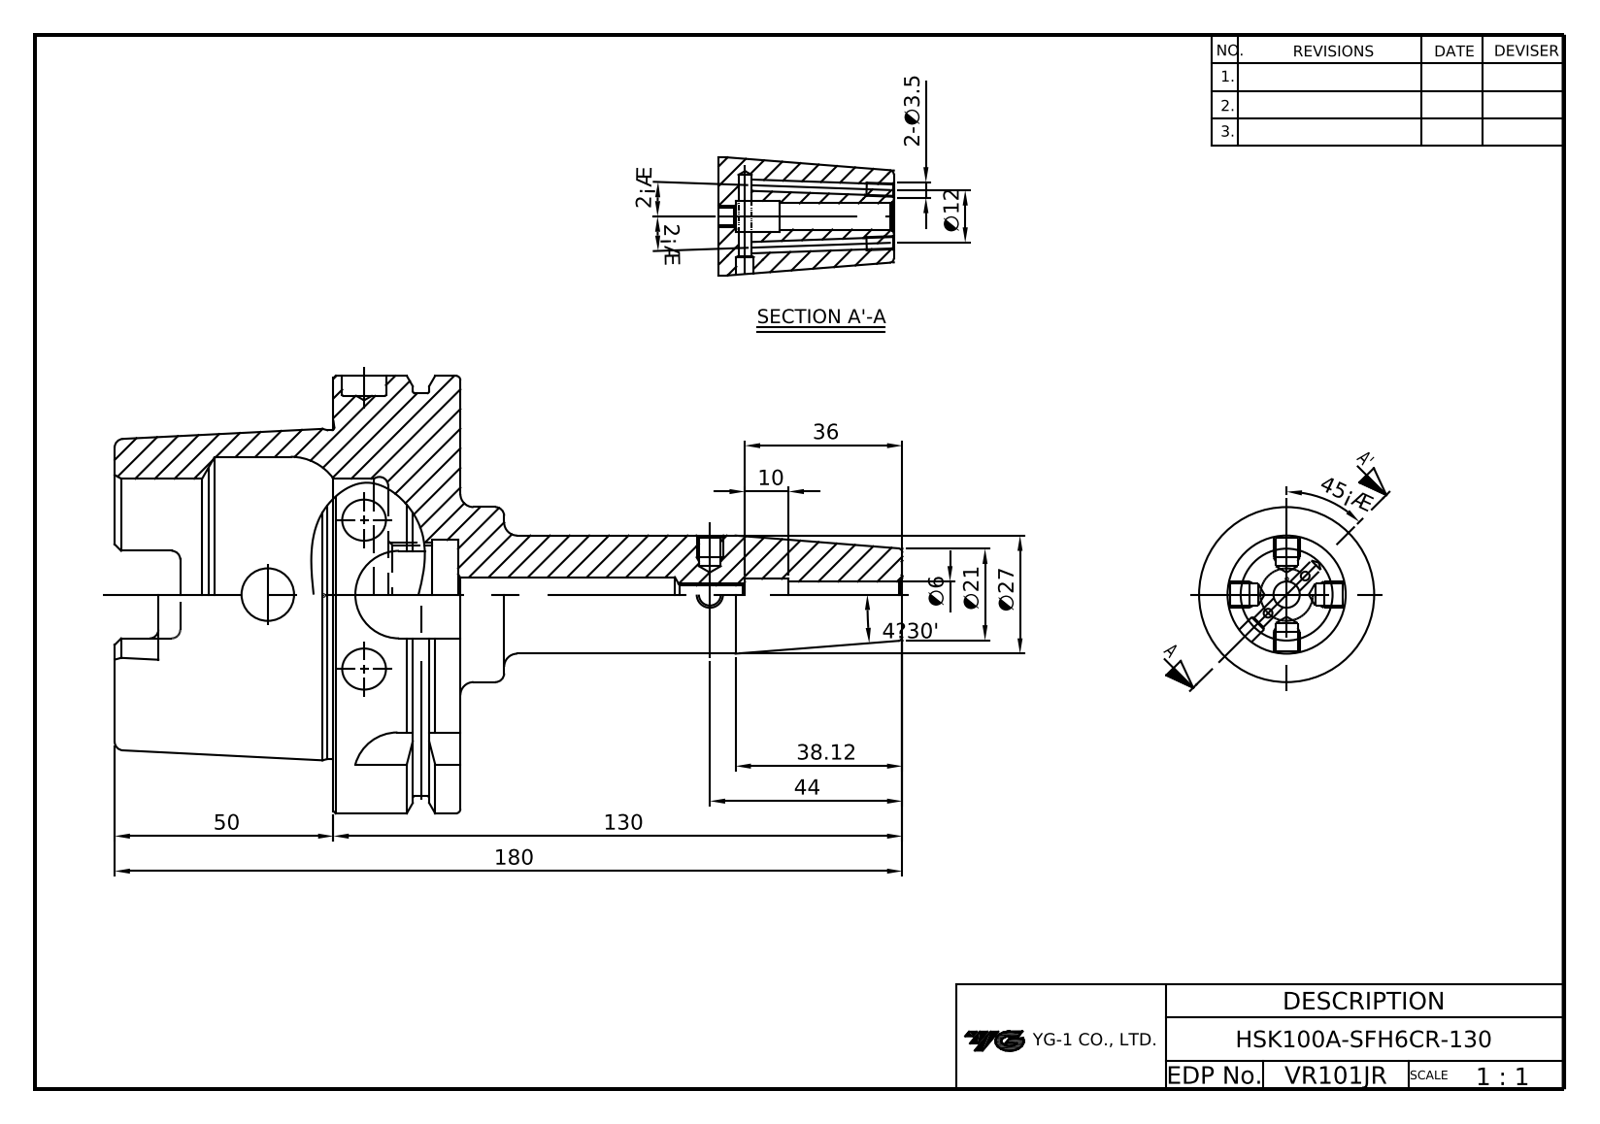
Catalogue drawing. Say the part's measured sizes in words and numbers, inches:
The part is named "LO-HSK100A-SFH6CR-130". Its 3-D file was written by "Autodesk Inventor 2024 (AUTOMOTIVE_DESIGN)". It is 1 solid with 124 faces: 39 planar, 38 cylindrical and 47 other. Overall it measures 7.087 by 3.937 by 3.937 inches. Its volume is 18.76 cubic inches and its surface area 94.51 square inches. Round holes: 2 of diameter 0.097, 2 of diameter 0.472, 1 of diameter 0.169, 1 of diameter 0.236, 1 of diameter 0.283, 1 of diameter 0.394, 1 of diameter 0.881, 1 of diameter 0.984, 1 of diameter 2.087, 1 of diameter 2.48. Round bosses or shafts: 1 of diameter 3.937, 1 of diameter 3.622, 1 of diameter 2.969, 1 of diameter 1.575, 1 of diameter 1.063. Partial cylindrical surfaces (rounded edges, fillets, slot ends): 6 of radius 0.079, 4 of radius 0.192, 4 of radius 0.394. The main face-to-face distances are 1.142, 0.492, 0.65, 3.11, 2.461, 1.969, 0.394, 3.465, 3.091, 1.122.
